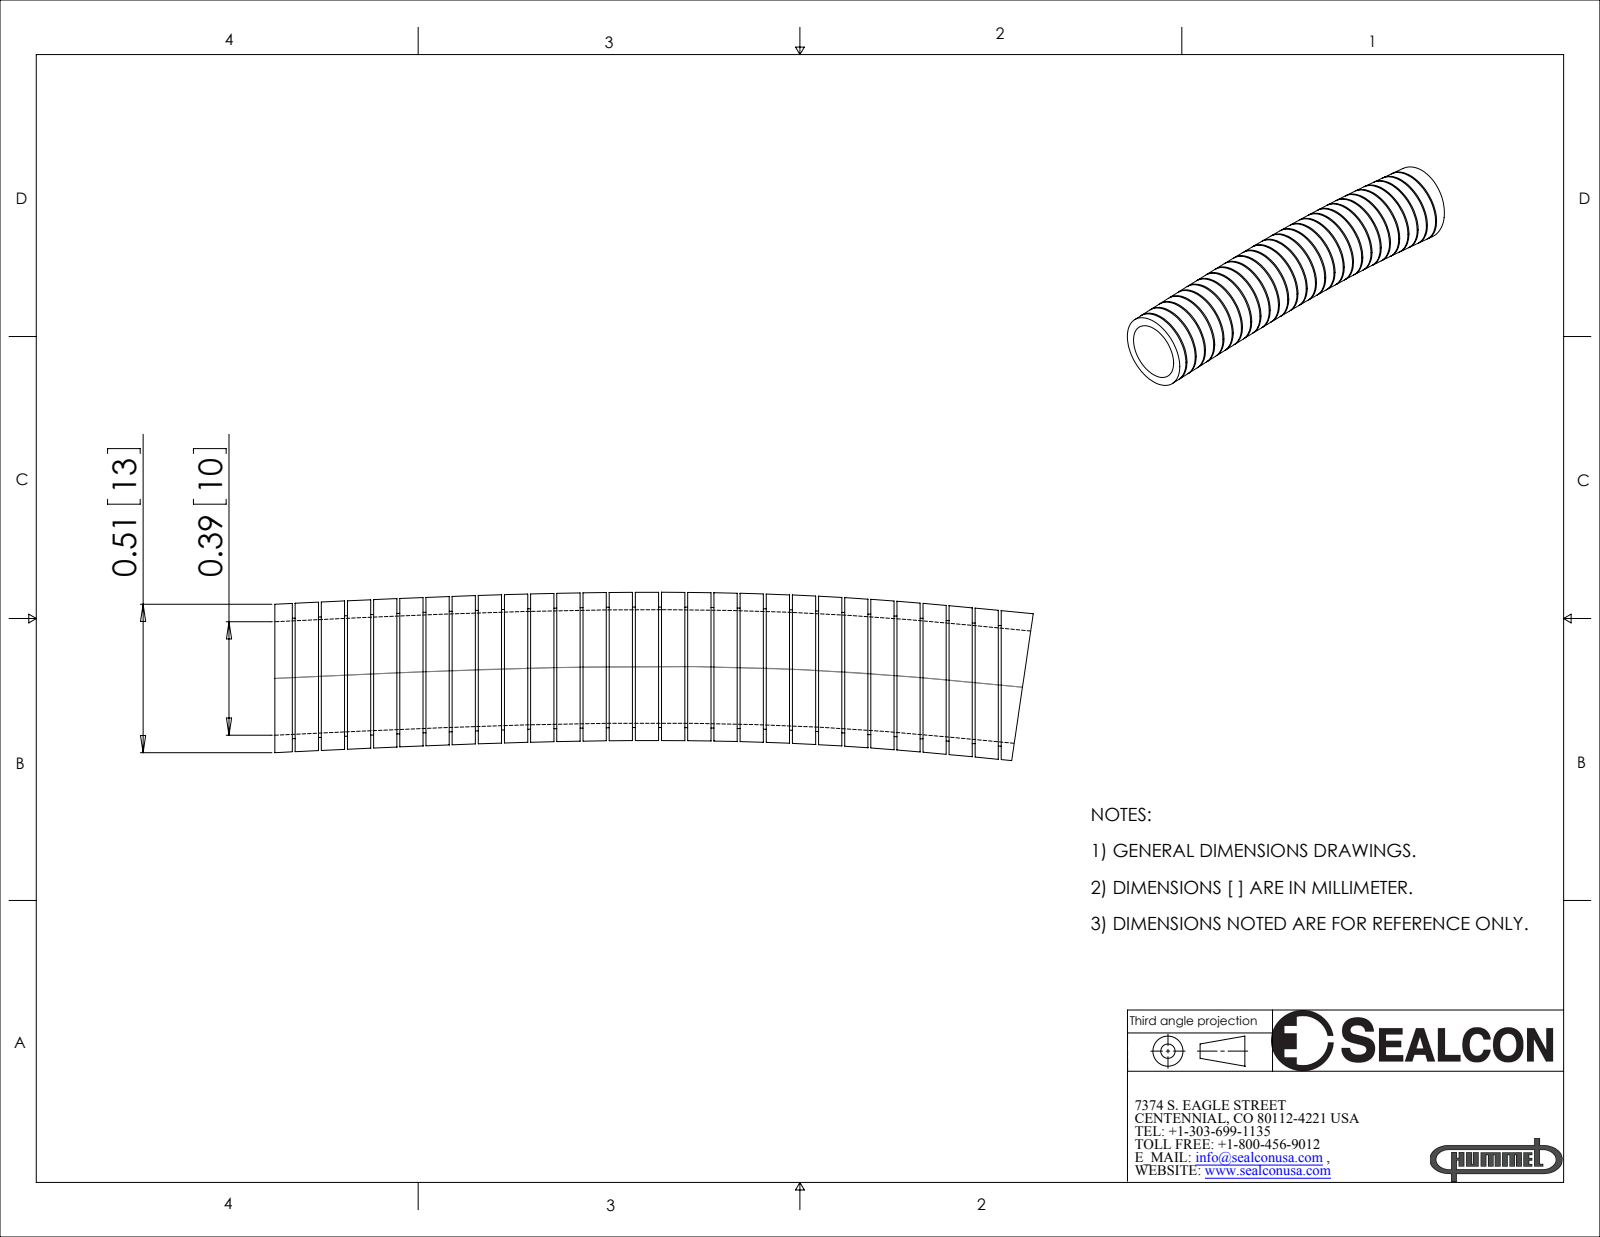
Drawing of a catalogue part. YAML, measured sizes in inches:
part_name: "SM-1013-HY"
step_written_by: "SolidWorks 2007 (AUTOMOTIVE_DESIGN)"
units: inches
bodies: {solids: 1, faces: 174, planar: 58, cylindrical: 56, other: 60}
overall_size: [2.607, 0.578, 0.51]
volume: 0.199
surface_area: 11.26
round_bosses_or_shafts:
  - {diameter: 0.414, count: 26}
face_to_face_distances: [0.09, 0.08, 0.18, 0.179, 0.269, 0.169, 0.359, 0.1, 0.269, 0.089]
